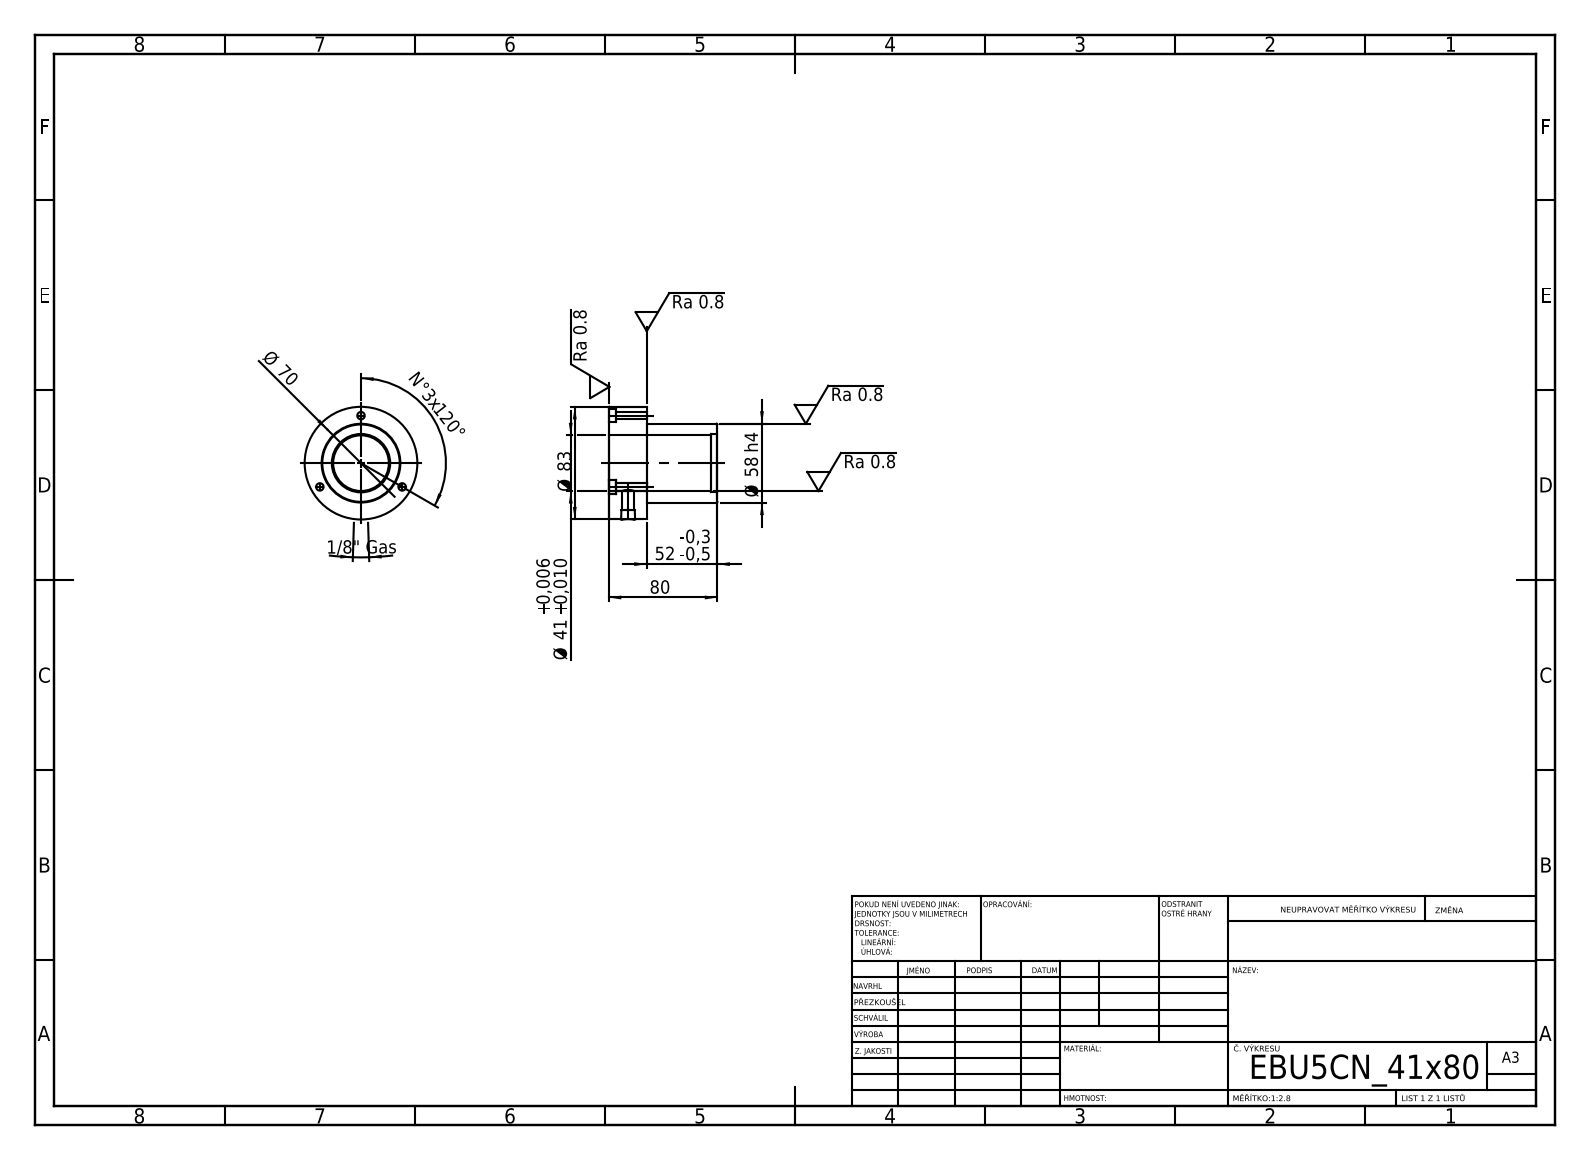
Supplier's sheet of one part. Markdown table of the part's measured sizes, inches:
| quantity | value |
| --- | --- |
| STEP written by | SolidWorks 2019 (CONFIG_CONTROL_DESIGN) |
| units | inches |
| bodies | 1 solid, 36 faces (8 planar, 22 cylindrical, 6 other) |
| overall size | 3.268 × 3.268 × 3.15 |
| volume | 10.88 in³ |
| surface area | 57.62 in² |
| round holes (diameter × count) | 0.217 × 3, 0.394 × 3, 0.332 × 1, 1.614 × 1, 1.693 × 1 |
| round bosses / shafts (diameter × count) | 3.268 × 1, 2.283 × 1 |
| main face-to-face distances | 1.102, 2.047, 3.15, 2.937, 0.89, 0.213, 0.197, 1.85, 2.74, 2.953 |
| hole center spacings | 1.378, 2.387 |
